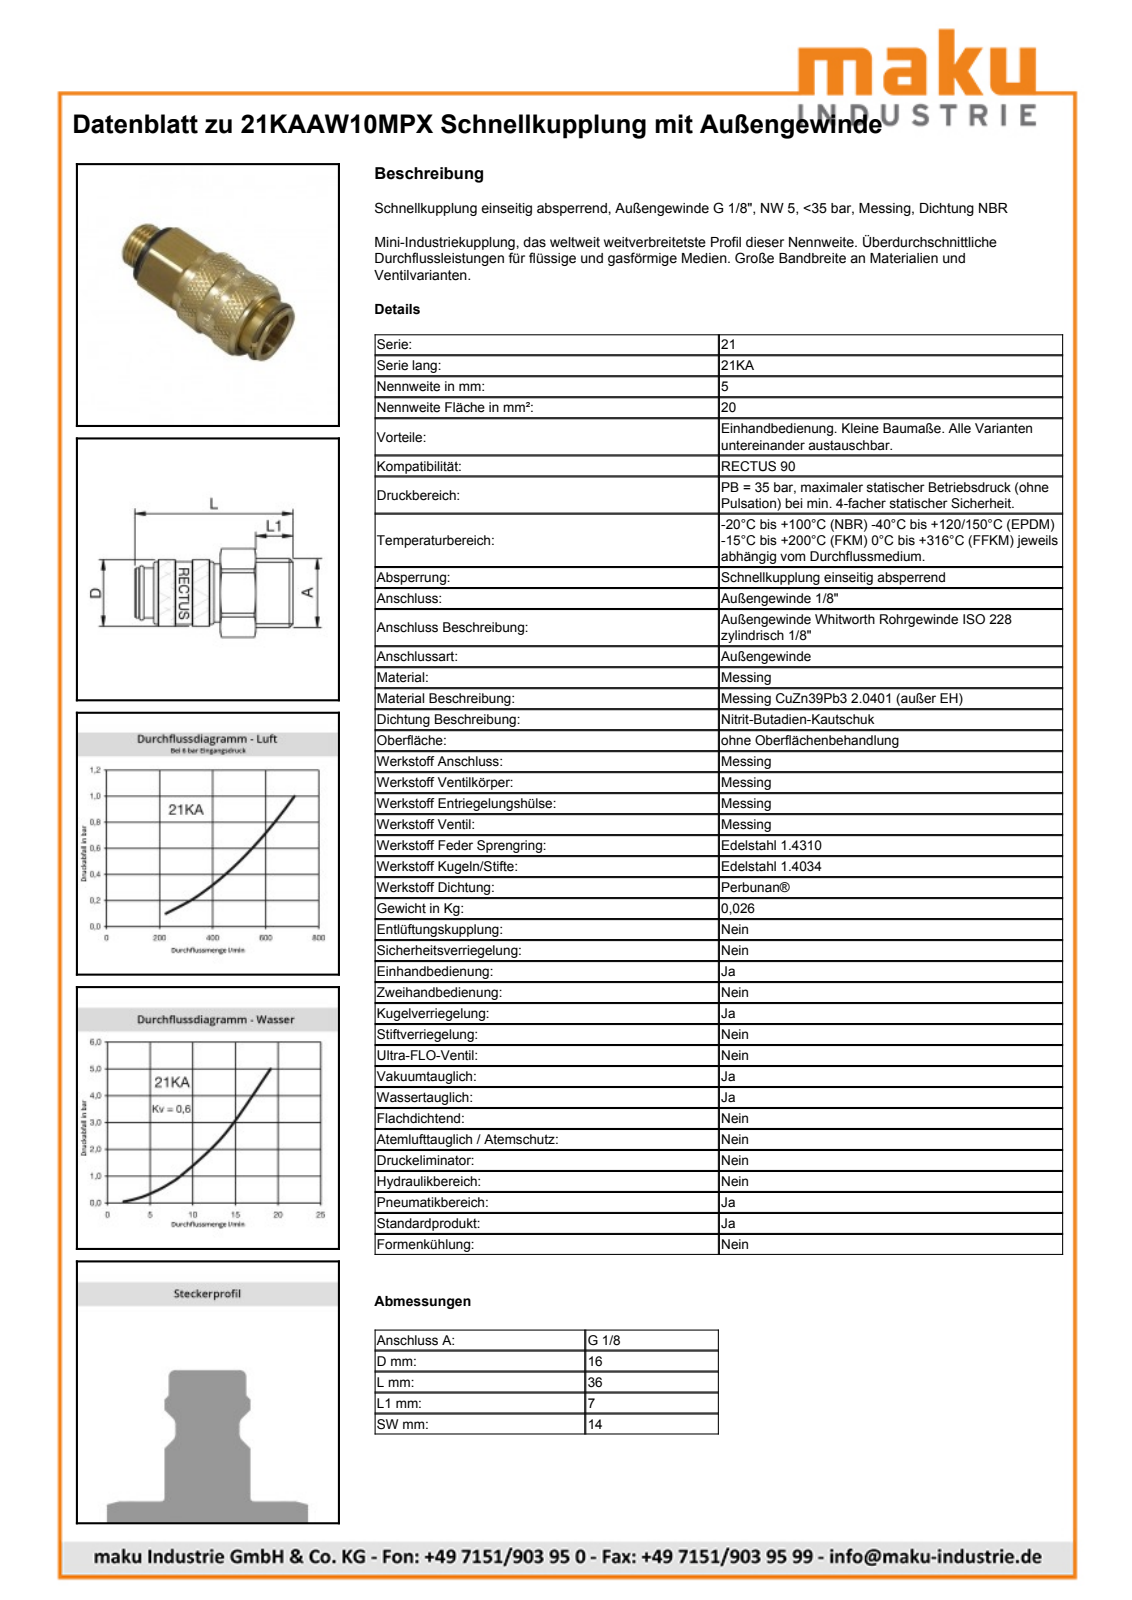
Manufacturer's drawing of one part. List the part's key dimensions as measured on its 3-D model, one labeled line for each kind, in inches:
Part name (STEP PRODUCT): D105314
STEP written by: Autodesk Inventor 2011 (AUTOMOTIVE_DESIGN)
Units: inches
Bodies: 2 solids, 462 faces (155 planar, 64 cylindrical, 243 other)
Overall size (bounding box): 1.423 × 0.636 × 0.636
Volume: 0.32 in³ · Surface area: 5.304 in²
Round holes (diameter × count): ⌀0.478 ×1, ⌀0.551 ×1
Round bosses / shafts (diameter × count): ⌀0.636 ×1, ⌀0.594 ×1, ⌀0.512 ×1, ⌀0.472 ×1, ⌀0.449 ×1, ⌀0.442 ×1, ⌀0.439 ×1, ⌀0.383 ×1
Partial cylindrical surfaces — rounded edges, fillets, slot ends (radius × count): R0.195 ×1, R0.293 ×1, R0.311 ×1
Main face-to-face distances: 0.551, 1.423, 1.207, 0.217, 0.571, 0.636, 0.787, 0.461, 0.175, 0.746
